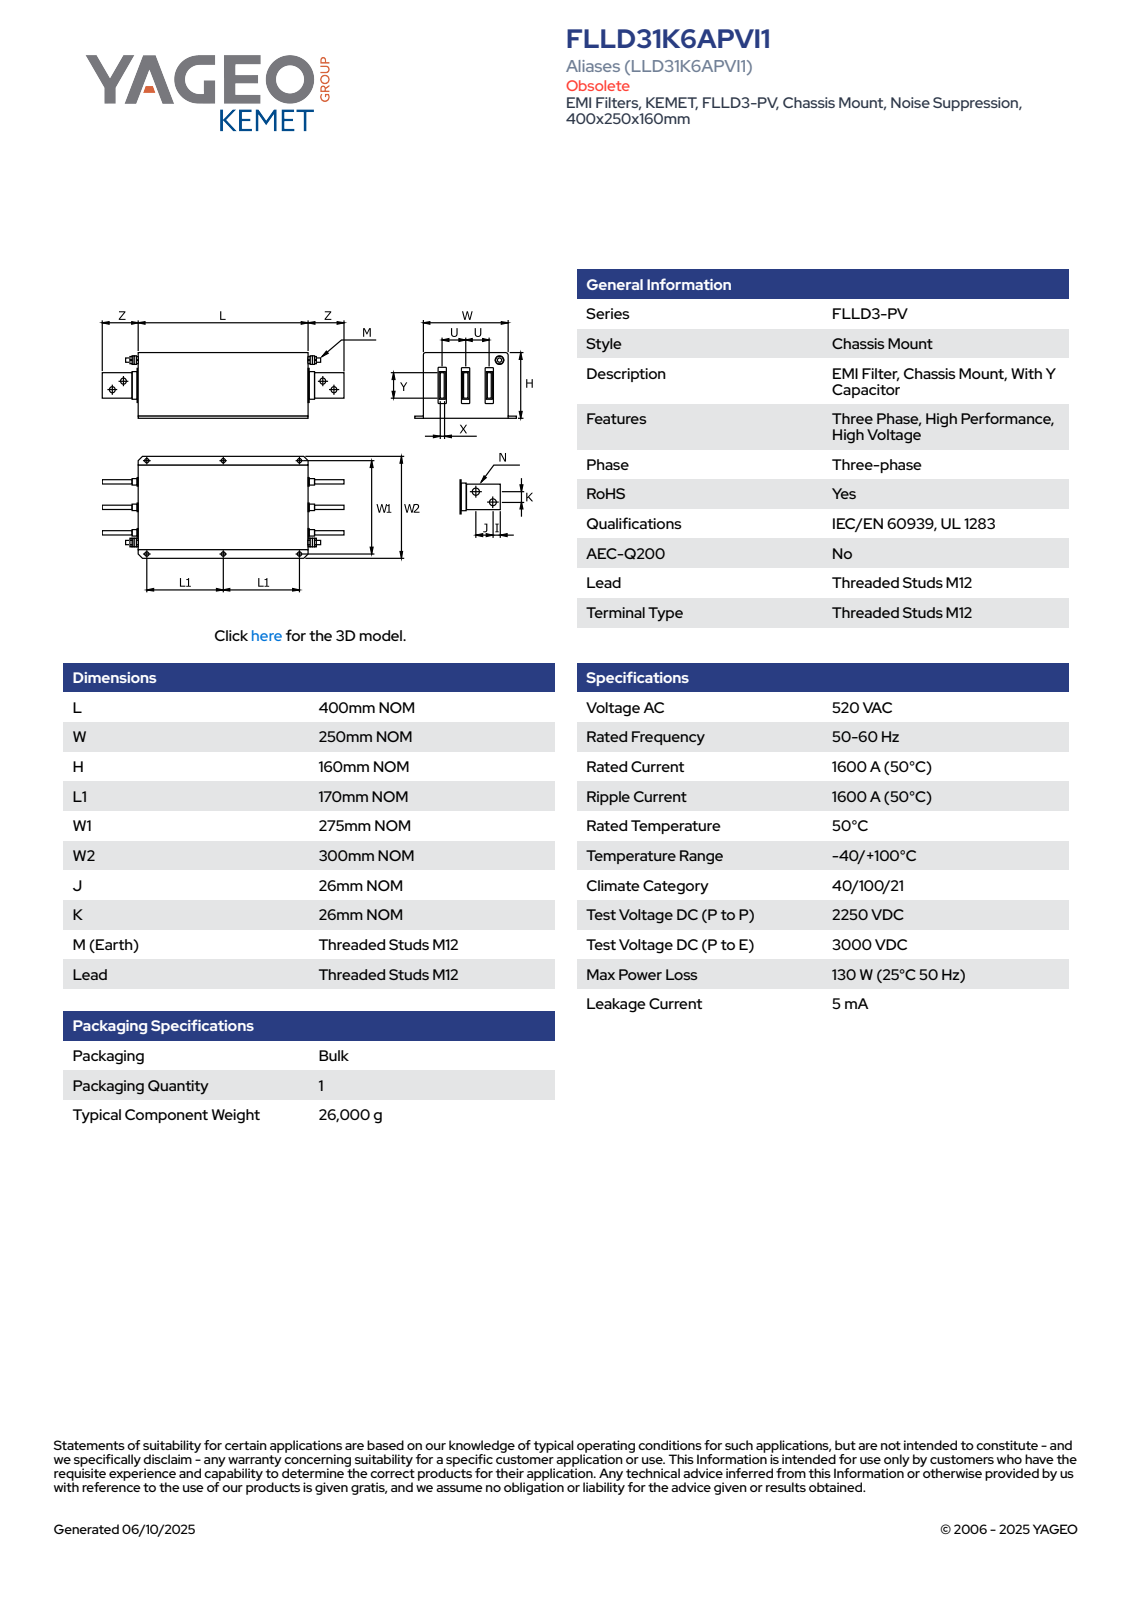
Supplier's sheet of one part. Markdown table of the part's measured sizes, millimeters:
| quantity | value |
| --- | --- |
| part name | Tank bush M4; Busbar 10x60^FLLD31K6APVI1_EXT; Rivet Ø3.2x4; 094-00241 Lid 1600A RevC (+8 more) |
| STEP written by | SolidWorks 2021 (AUTOMOTIVE_DESIGN) |
| units | millimeters |
| bodies | 88 solids, 2996 faces (744 planar, 918 cylindrical, 1334 other) |
| overall size | 590 × 300 × 160 |
| volume | 1 193 000 mm³ |
| surface area | 1 093 000 mm² |
| round holes (diameter × count) | 1.8 × 20, 3.4 × 14, 3.2 × 10, 12 × 6, 14 × 5, 5 × 4, 5.2 × 4, 13 × 1 |
| round bosses / shafts (diameter × count) | 3.2 × 14, 7 × 4, 24 × 1, 12 × 1 |
| partial cylindrical surfaces (radius × count) | 2 × 60, 1 × 42, 0.2 × 36, 0.25 × 24, 0.5 × 20, 2.5 × 10, 1.5 × 4, 3 × 2 |
| main face-to-face distances | 2, 1, 248, 158, 398, 160, 157, 159, 60, 396 |
| hole center spacings | 60, 81.25, 108.17, 116.3, 137.94, 170, 227.3, 323.3 |
